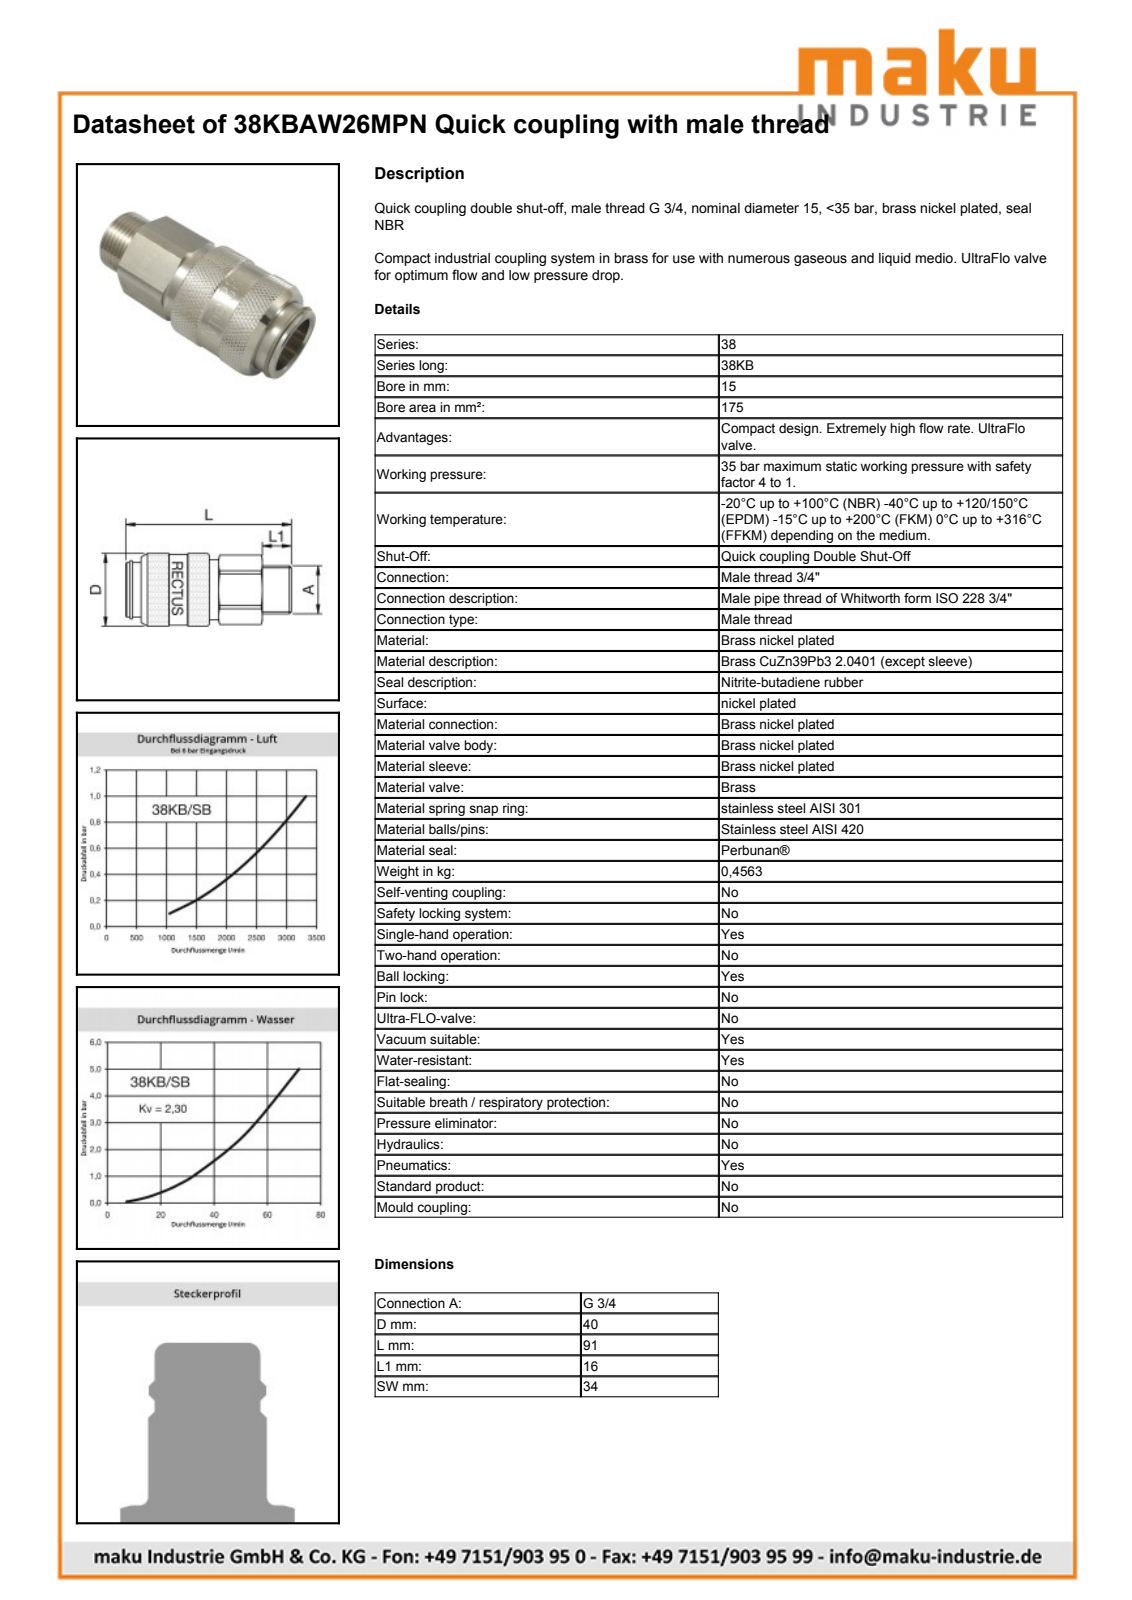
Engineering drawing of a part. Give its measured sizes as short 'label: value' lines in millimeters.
name: D110643
written by: Autodesk Inventor 2013 (AUTOMOTIVE_DESIGN)
unit: mm
bodies: 2 solids, 518 faces (185 planar, 75 cylindrical, 258 other)
size: 91.25 × 40 × 40
volume: 85 040 mm³; area: 21 038 mm²
holes: 1× ⌀28.95, 1× ⌀30, 1× ⌀30.75, 1× ⌀34.45, 1× ⌀34.6
bosses: 1× ⌀40, 1× ⌀39, 1× ⌀34, 1× ⌀28.5, 1× ⌀27.81, 1× ⌀26.44
rounds: 1× R18.5, 1× R19.4
face distances: 34, 16, 91.25, 75.25, 45.6, 8.15, 67.1, 83.1, 40.25, 32.1
